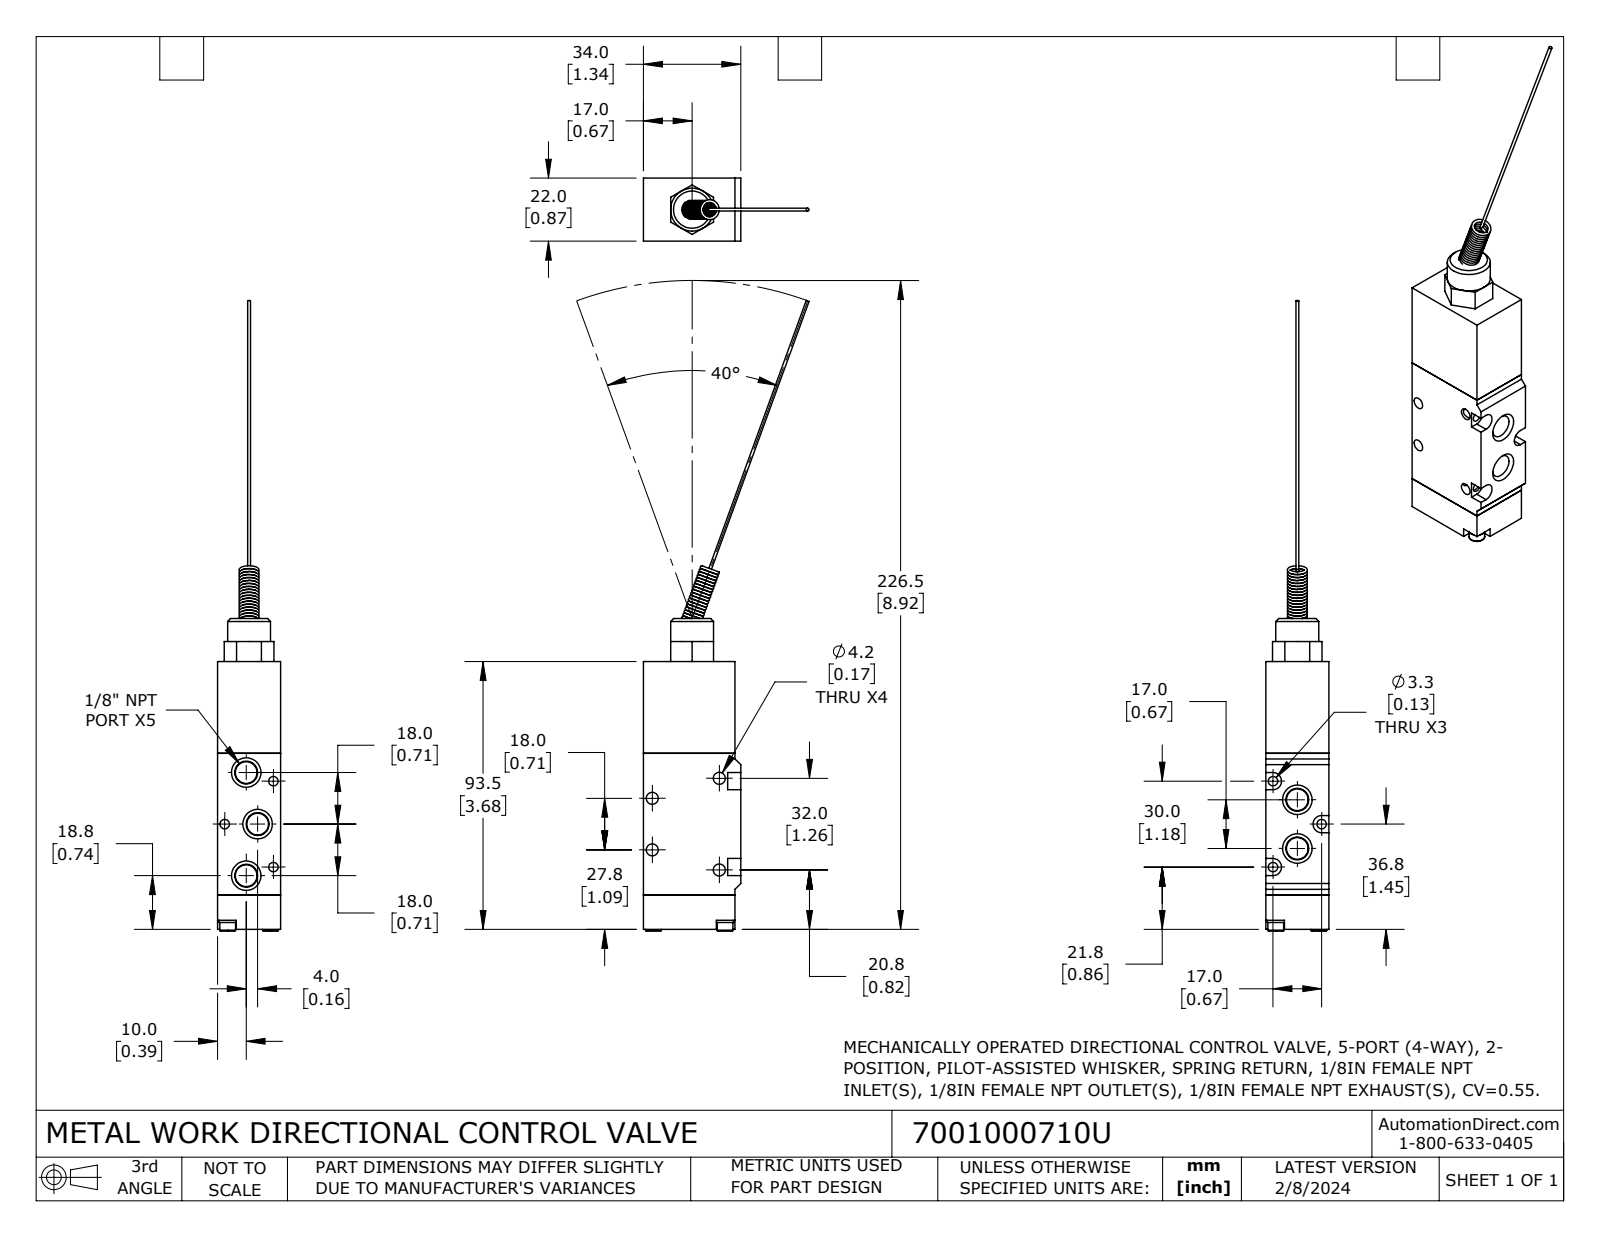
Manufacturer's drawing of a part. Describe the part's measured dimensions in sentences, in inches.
The part is named "7001000710U". Its 3-D file was written by "SolidWorks 2023 (CONFIG_CONTROL_DESIGN)". It is 8 solids with 394 faces: 90 planar, 125 cylindrical and 179 other. Overall it measures 8.668 by 2.277 by 0.866 inches. Its volume is 4.069 cubic inches and its surface area 31.31 square inches. Round holes: 4 of diameter 0.165, 3 of diameter 0.13, 2 of diameter 0.118, 1 of diameter 0.235. Round bosses or shafts: 2 of diameter 0.236, 2 of diameter 0.217, 2 of diameter 0.039, 1 of diameter 0.591, 1 of diameter 0.238. Partial cylindrical surfaces (rounded edges, fillets, slot ends): 3 of radius 0.118. The main face-to-face distances are 0.866, 1.26, 1.949, 0.079, 1.339, 0.472, 2.421, 3.681, 3.209, 0.591. The hole center spacings are 0.893, 0.961, 1.348, 0.709, 1.148, 1.181, 1.26.
